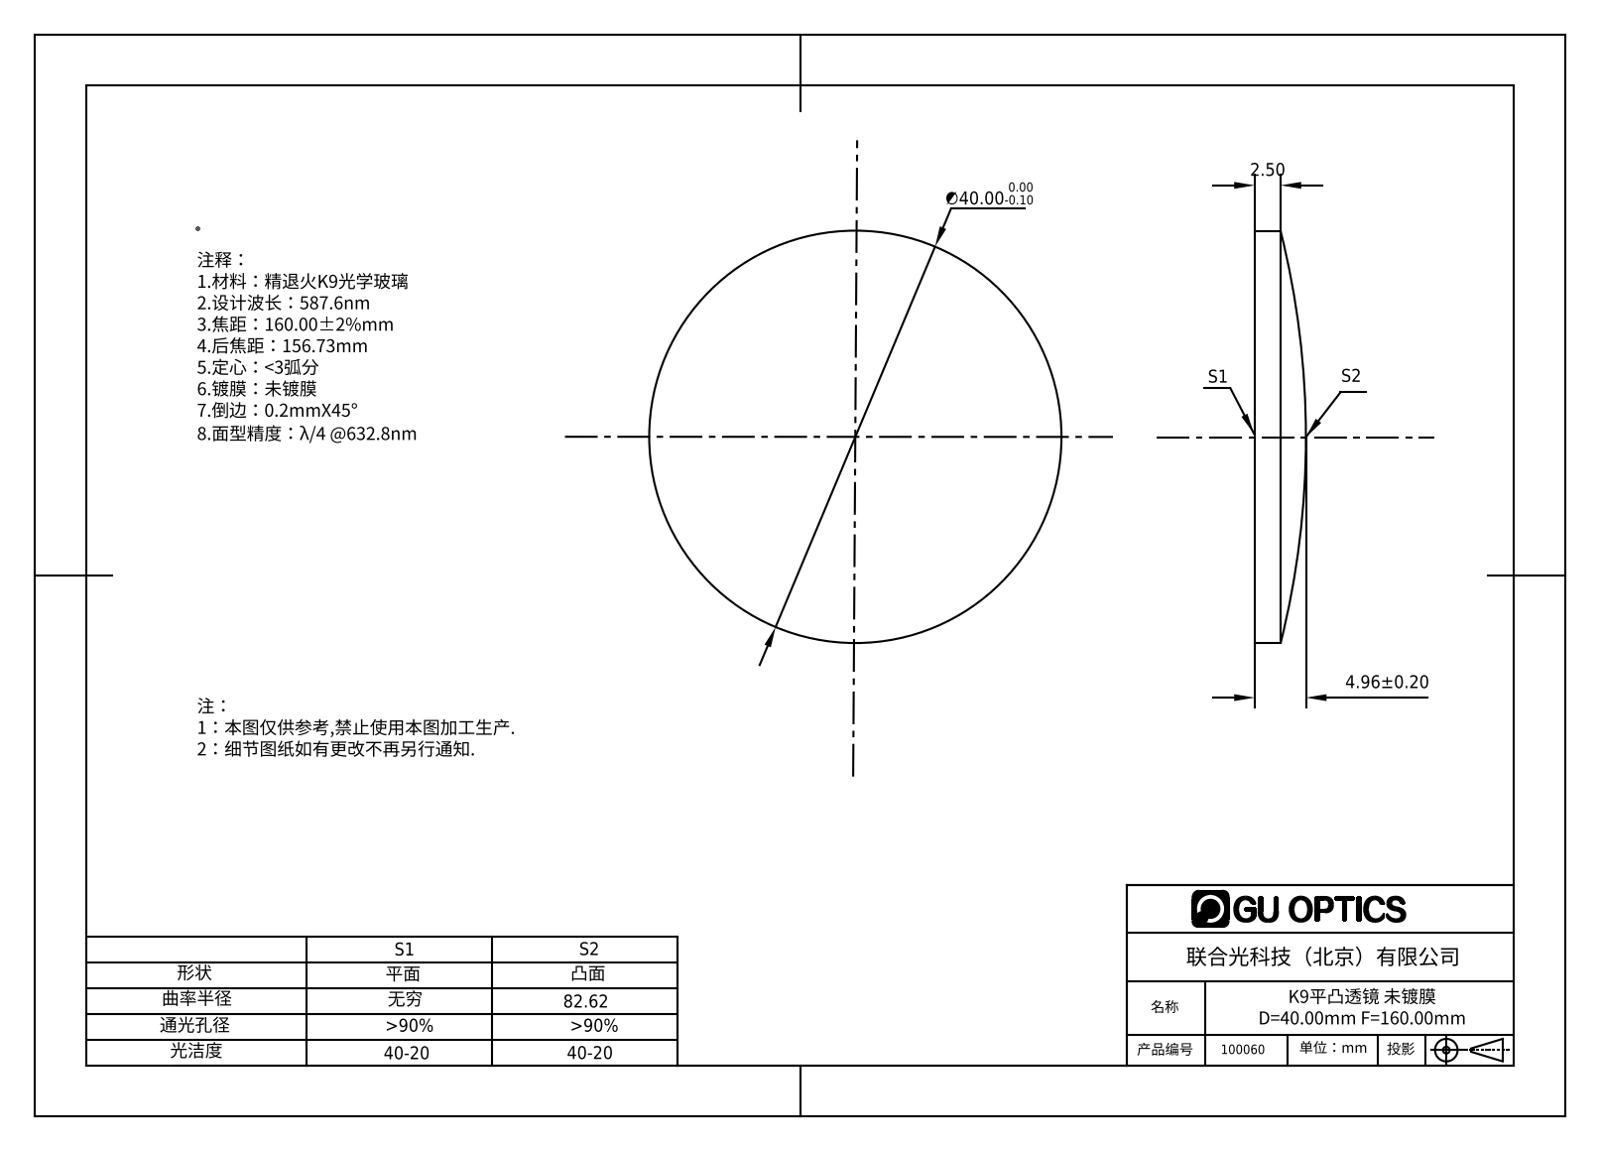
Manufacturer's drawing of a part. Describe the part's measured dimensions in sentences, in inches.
The part is named "100060". Its 3-D file was written by "SolidWorks 2016 (AUTOMOTIVE_DESIGN)". It is 1 solid with 5 faces: 1 planar, 2 cylindrical and 2 other. Overall it measures 1.575 by 1.575 by 0.195 inches. Its volume is 0.287 cubic inches and its surface area 4.411 square inches. Round bosses or shafts: 1 of diameter 1.575.
